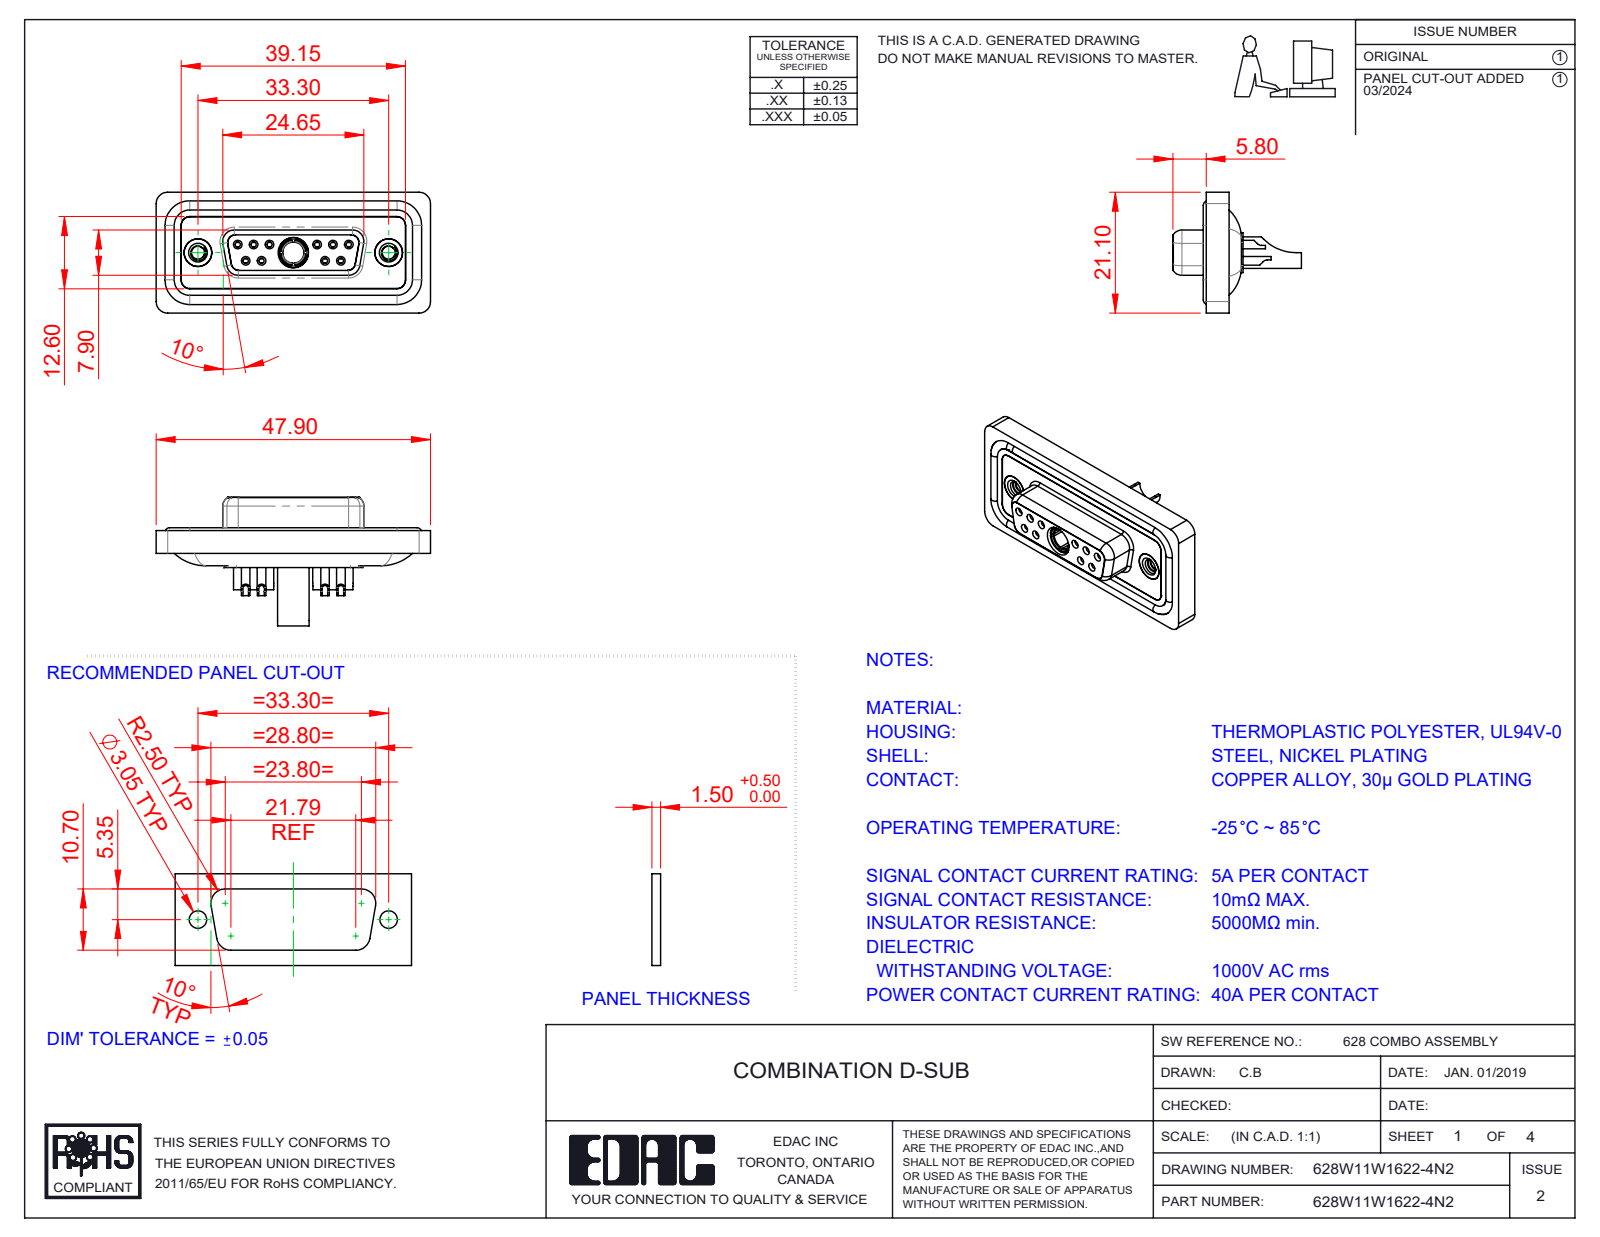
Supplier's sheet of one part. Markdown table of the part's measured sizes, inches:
| quantity | value |
| --- | --- |
| part name | 628Combo Contact Row 2_22; 628Combo Shell Rear_15 Contacts; 628Combo Waterproof Housing_15 Contacts; 628Combo Contact Row 1_22 (+5 more) |
| STEP written by | SolidWorks 2023 (CONFIG_CONTROL_DESIGN) |
| units | inches |
| bodies | 19 solids, 1013 faces (306 planar, 422 cylindrical, 285 other) |
| overall size | 1.886 × 0.884 × 0.831 |
| volume | 0.377 in³ |
| surface area | 15.92 in² |
| round holes (diameter × count) | 0.035 × 10, 0.039 × 10, 0.043 × 10, 0.059 × 10, 0.079 × 10, 0.067 × 6, 0.063 × 4, 0.191 × 3, 0.089 × 2, 0.157 × 2, 0.159 × 2, 0.197 × 2 |
| round bosses / shafts (diameter × count) | 0.087 × 10, 0.063 × 10, 0.195 × 2, 0.189 × 2, 0.217 × 1, 0.205 × 1, 0.195 × 1, 0.187 × 1 |
| partial cylindrical surfaces (radius × count) | 0.059 × 22, 0.079 × 20, 0.053 × 12, 0.063 × 8, 0.039 × 6, 0.01 × 4, 0.02 × 4, 0.024 × 4 |
| main face-to-face distances | 0.016, 0.063, 0.071, 0.114, 0.02, 0.043, 0.222, 0.293, 0.26, 0.278 |
| hole center spacings | 0.124, 0.109, 0.545, 0.436, 0.654, 0.198, 0.198, 0.218 |
